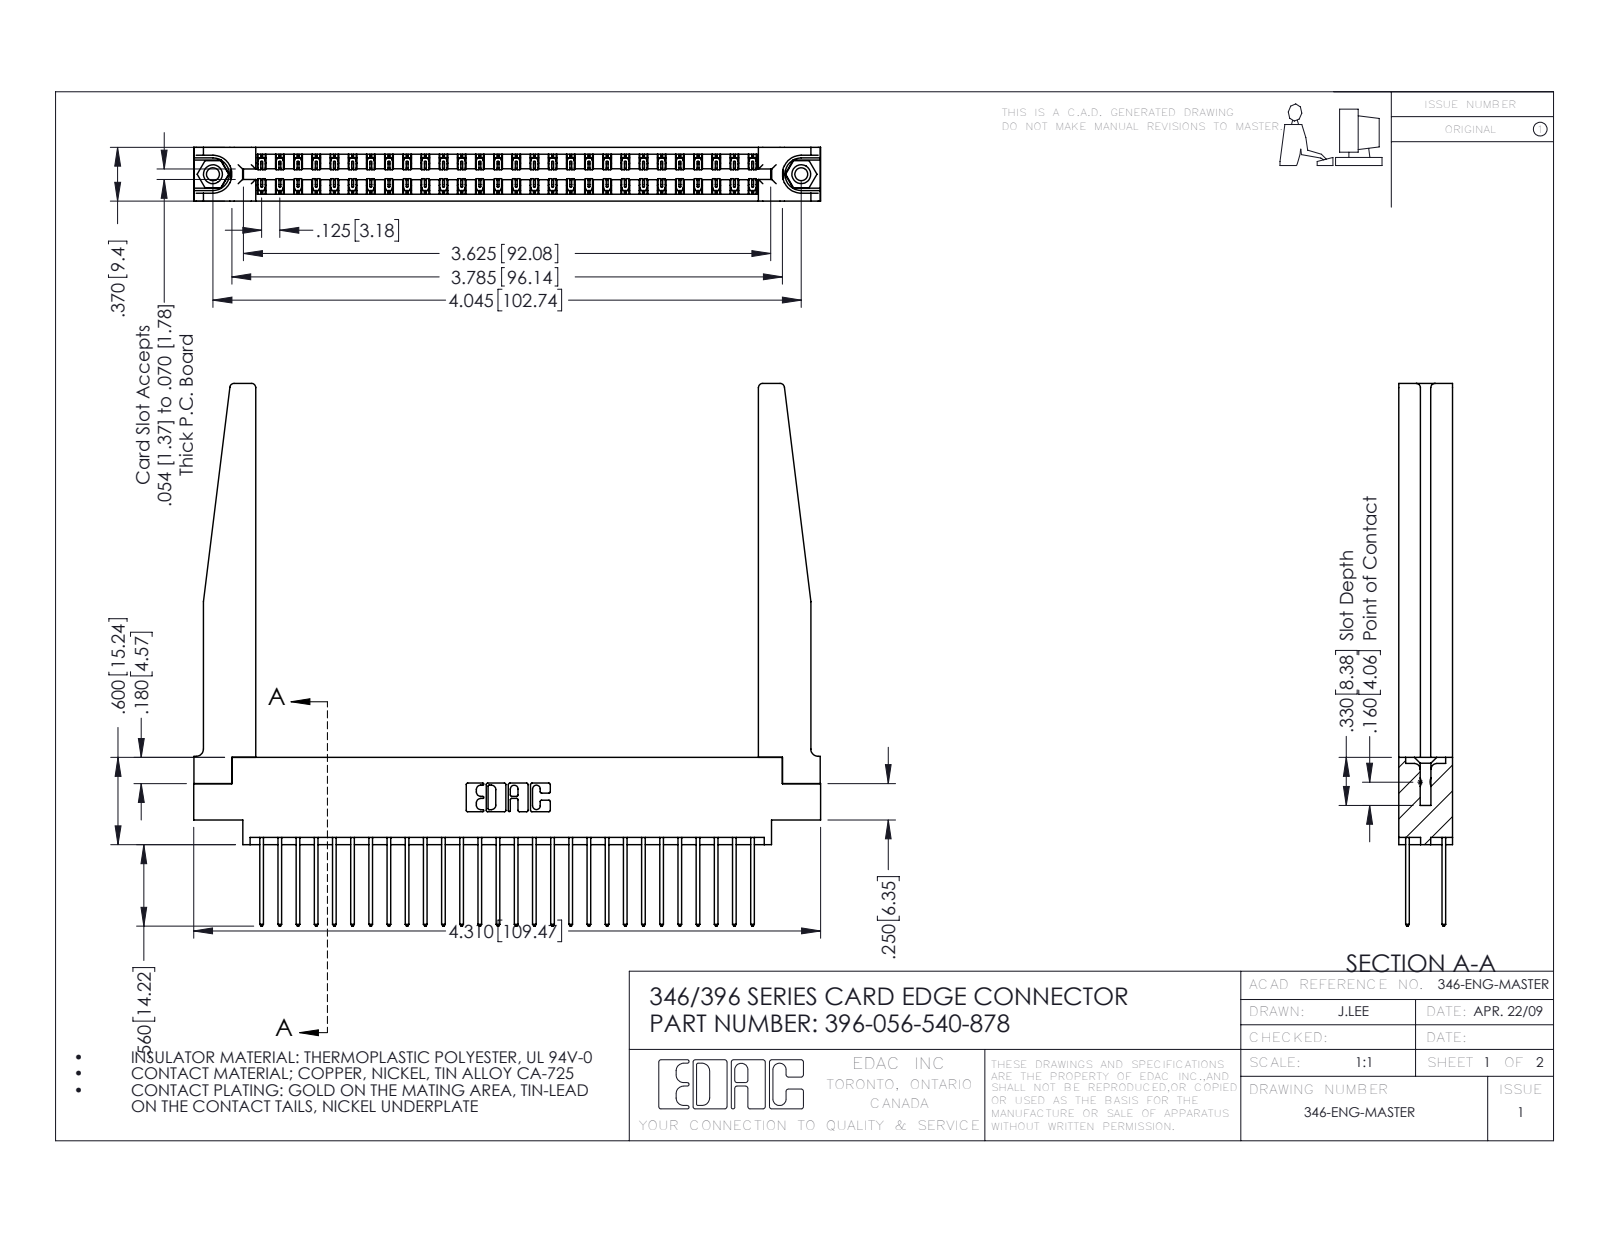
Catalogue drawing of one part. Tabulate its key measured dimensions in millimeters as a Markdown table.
| quantity | value |
| --- | --- |
| part name | 345-292-001_345-293-140; 346 Part_0.170 Offset - 0.156 Dia-TH; 396-056-540-878; 345-250-001_345-250-001-102 (+1 more) |
| STEP written by | SolidWorks 2016 (CONFIG_CONTROL_DESIGN) |
| units | millimeters |
| bodies | 61 solids, 3272 faces (2182 planar, 1038 cylindrical, 52 other) |
| overall size | 109.5 × 94.7 × 9.4 |
| volume | 17 530 mm³ |
| surface area | 22 100 mm² |
| round holes (diameter × count) | 2.3 × 2, 3.2 × 2, 4 × 2, 1.6 × 1 |
| round bosses / shafts (diameter × count) | 3.9 × 2 |
| partial cylindrical surfaces (radius × count) | 0.2 × 84, 0.3 × 56, 0.3 × 22, 0.8 × 8, 0.2 × 6, 0.8 × 6, 0.7 × 3, 0.4 × 2 |
| main face-to-face distances | 9.4, 1.2, 8.2, 1.8, 6.4, 7.6, 0.6, 3.8, 3.8, 7 |
| hole center spacings | 6.2, 97.5, 102.7 |
